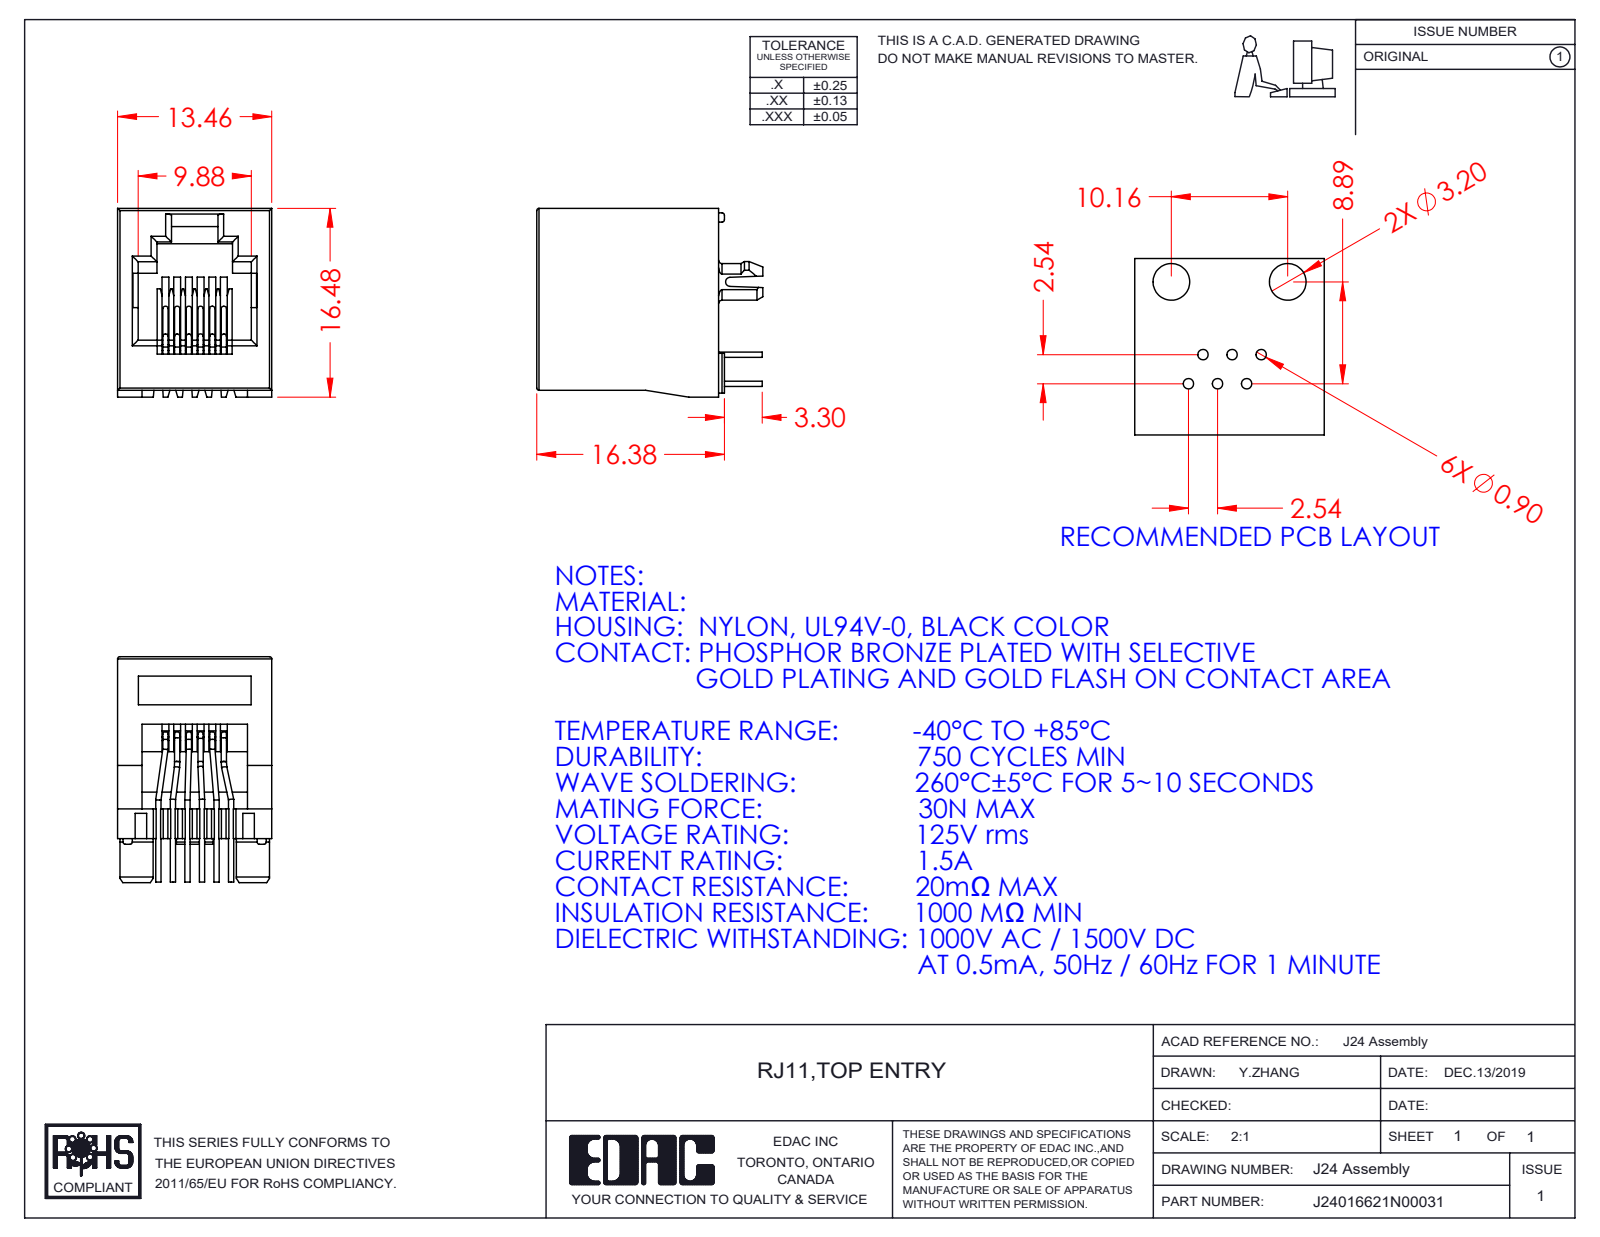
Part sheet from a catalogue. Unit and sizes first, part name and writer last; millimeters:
Units: millimetres
Overall size (bounding box): 19.73 × 16.48 × 13.46
Round holes (diameter × count): ⌀0.46 ×6, ⌀2.1 ×2
Round bosses / shafts (diameter × count): ⌀0.46 ×26
Partial cylindrical surfaces — rounded edges, fillets, slot ends (radius × count): R0.5 ×16, R0.2 ×10, R0.32 ×6, R0.34 ×6, R0.25 ×3, R1.6 ×2, R1.77 ×2, R0.4 ×1
Main face-to-face distances: 13.46, 1.02, 1.79, 11.67, 0.6, 15.87, 8.24, 3.43, 10.03, 1.64
Hole centre spacings: 2.84, 2.54, 4.58, 5.08, 13.1, 6.84, 10.16, 10.35
Volume: 1 745 mm³ · Surface area: 2 930 mm²
Bodies: 7 solids, 444 faces (256 planar, 150 cylindrical, 38 other)
Part name (STEP PRODUCT): 24 Insulator_Standard; 24 Contacts_Standard; RJ24016621N00031
STEP written by: SolidWorks 2016 (CONFIG_CONTROL_DESIGN)
